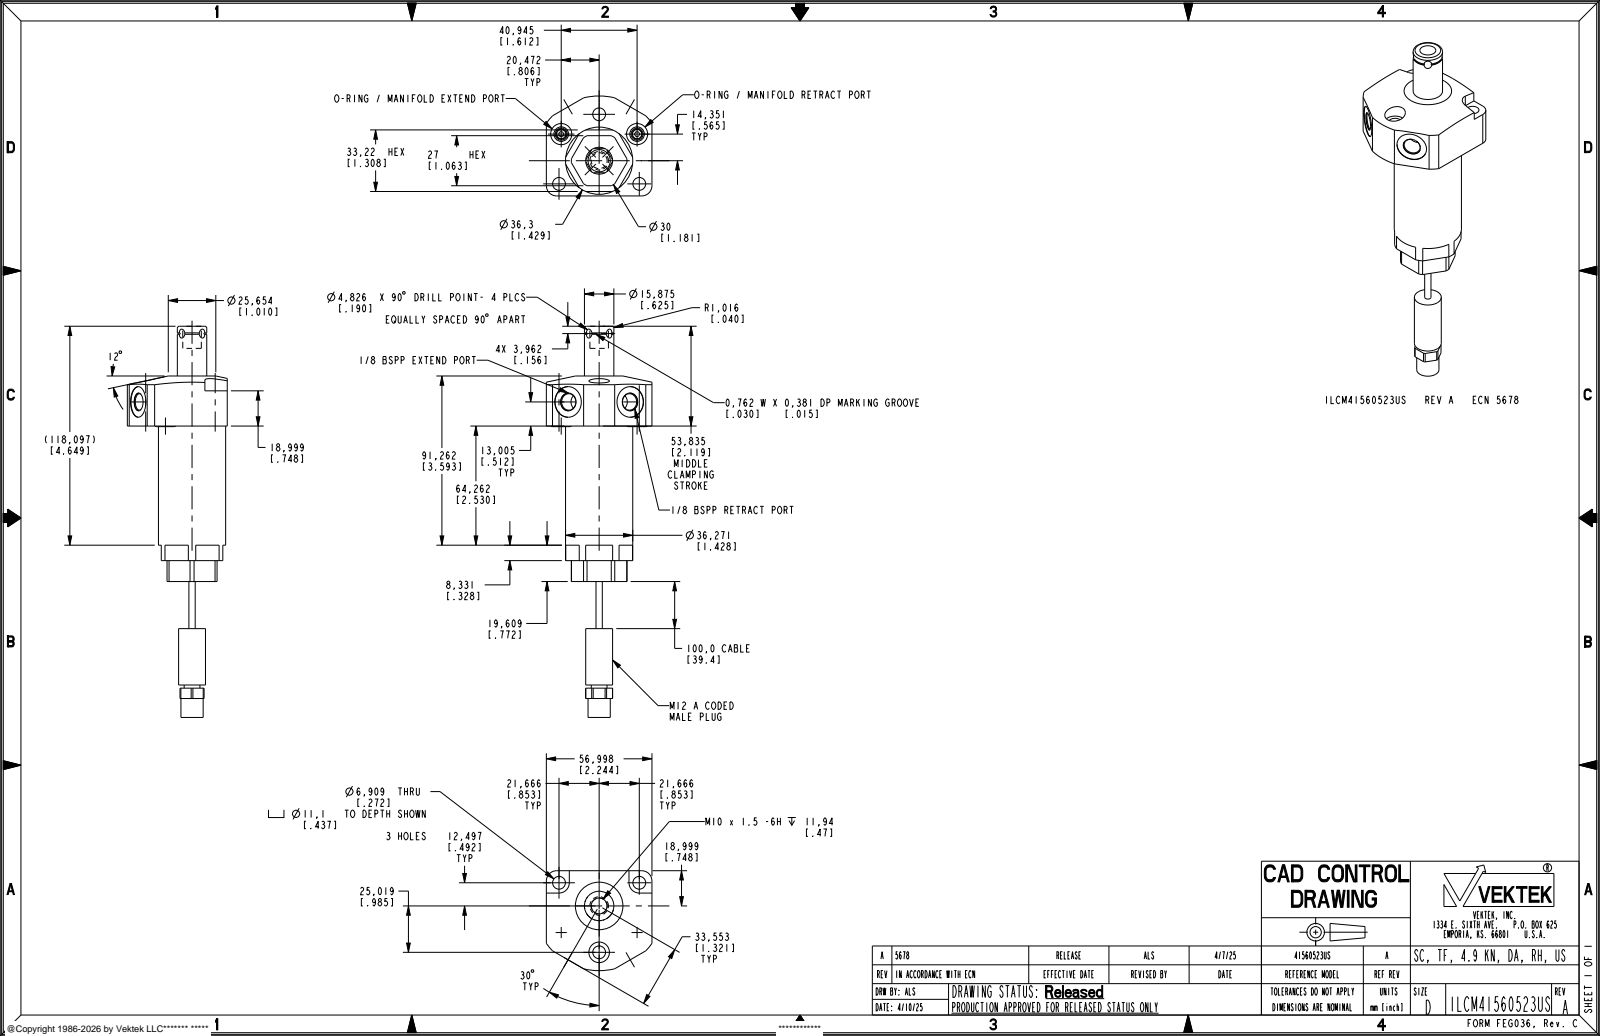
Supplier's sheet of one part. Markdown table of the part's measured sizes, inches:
| quantity | value |
| --- | --- |
| part name | ILCM41560523US |
| STEP written by | CREO PARAMETRIC BY PTC INC, 2021164 (AUTOMOTIVE_DESIGN) |
| units | inches |
| bodies | 1 solid, 192 faces (87 planar, 75 cylindrical, 30 other) |
| overall size | 8.307 × 2.444 × 2.373 |
| volume | 9.544 in³ |
| surface area | 43.47 in² |
| round holes (diameter × count) | 0.272 × 3, 0.098 × 2, 0.256 × 2, 0.348 × 2, 0.449 × 2, 0.65 × 2, 0.339 × 1, 0.437 × 1, 0.895 × 1 |
| round bosses / shafts (diameter × count) | 0.216 × 2, 1.428 × 1, 0.625 × 1, 0.571 × 1, 0.472 × 1, 0.394 × 1, 0.335 × 1, 0.134 × 1 |
| partial cylindrical surfaces (radius × count) | 0.219 × 2, 0.219 × 2, 0.298 × 1, 0.591 × 1, 1.375 × 1 |
| main face-to-face distances | 1.063, 2.244, 0.122, 1.185, 3.302, 0.772, 2.53, 0.832, 0.06, 2.47 |
| hole center spacings | 0.985, 0.909, 0.984, 1.058, 1.706, 1.967, 1.612, 1.706 |
